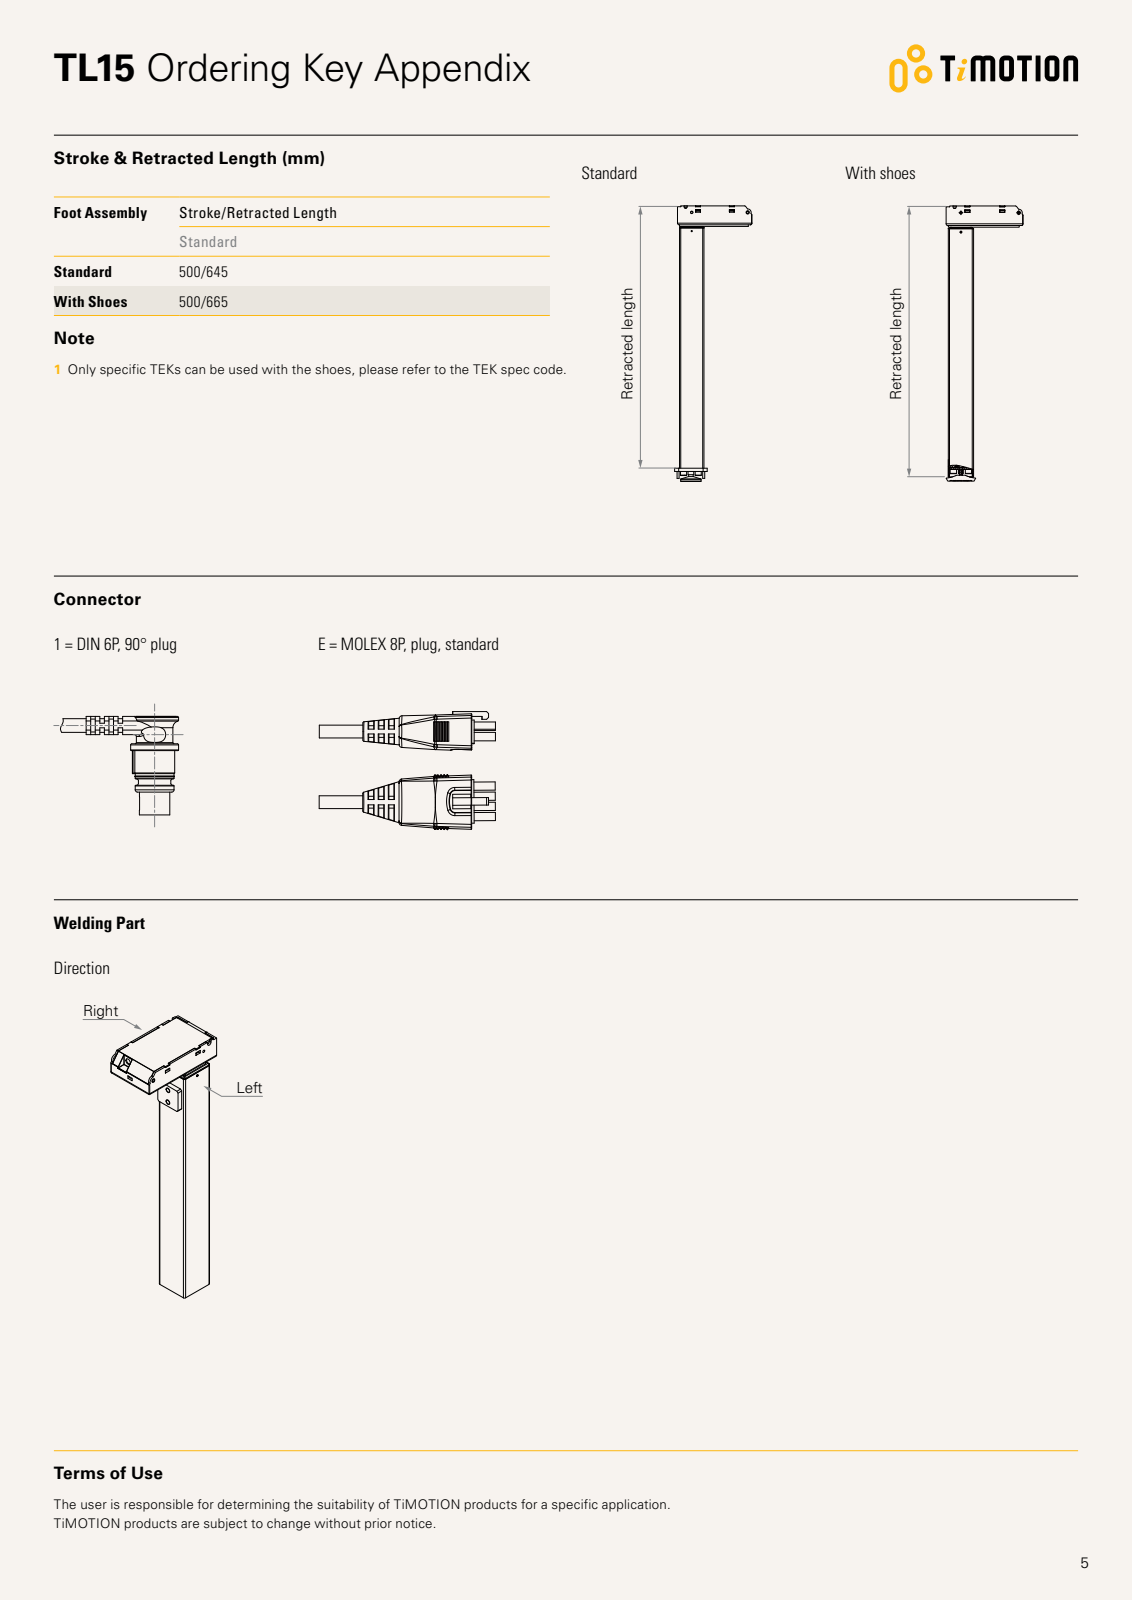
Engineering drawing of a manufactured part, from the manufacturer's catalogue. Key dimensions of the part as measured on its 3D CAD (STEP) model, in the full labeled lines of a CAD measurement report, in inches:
Part name (STEP PRODUCT): 產品三維模型圖-TL15（標準）-A.LSDPRT-1
STEP written by: SolidWorks 2015 (CONFIG_CONTROL_DESIGN)
Units: inches
Bodies: 2 solids, 472 faces (262 planar, 148 cylindrical, 62 other)
Overall size (bounding box): 25.394 × 7.303 × 4.213
Volume: 228.8 in³ · Surface area: 433.4 in²
Round holes (diameter × count): ⌀0.335 ×4, ⌀0.197 ×2, ⌀0.205 ×2, ⌀0.315 ×1
Round bosses / shafts (diameter × count): ⌀0.315 ×3, ⌀0.197 ×3, ⌀0.551 ×1, ⌀0.276 ×1
Partial cylindrical surfaces — rounded edges, fillets, slot ends (radius × count): R0.012 ×40, R0.02 ×13, R0.118 ×9, R0.039 ×7, R0.059 ×6, R0.157 ×4, R0.079 ×2, R0.177 ×1
Main face-to-face distances: 2.362, 3.15, 0.157, 0.169, 0.492, 3.642, 0.335, 3.965, 0.323, 3.472
Hole centre spacings: 1.002, 1.417, 0.748, 1.594, 1.616, 2.004, 2.165, 2.583
